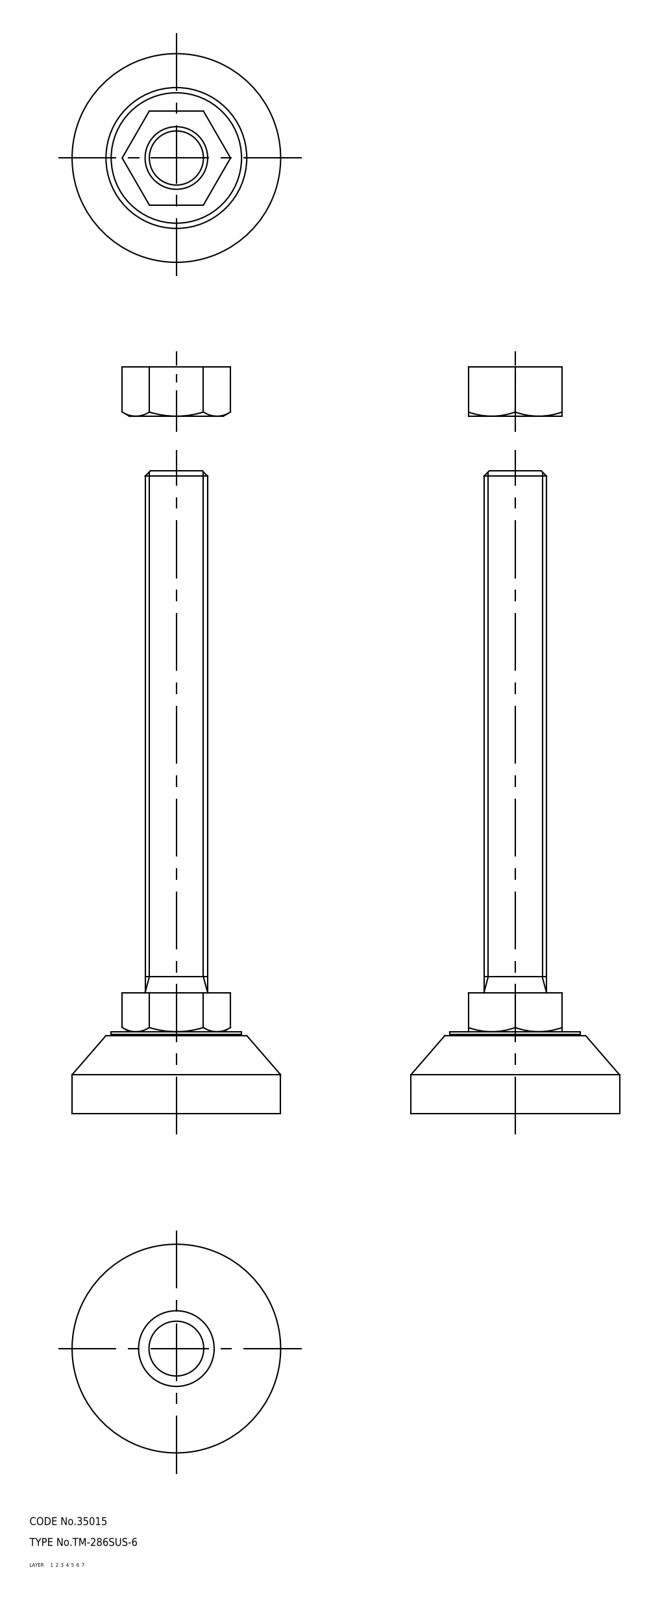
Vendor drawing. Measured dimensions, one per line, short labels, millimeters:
name: 67111650; 67111663
written by: CADfix (AUTOMOTIVE_DESIGN)
unit: mm
bodies: 2 solids, 52 faces (0 planar, 0 cylindrical, 52 other)
size: 246.5 × 80 × 80
volume: 248 476 mm³; area: 39 939 mm²
